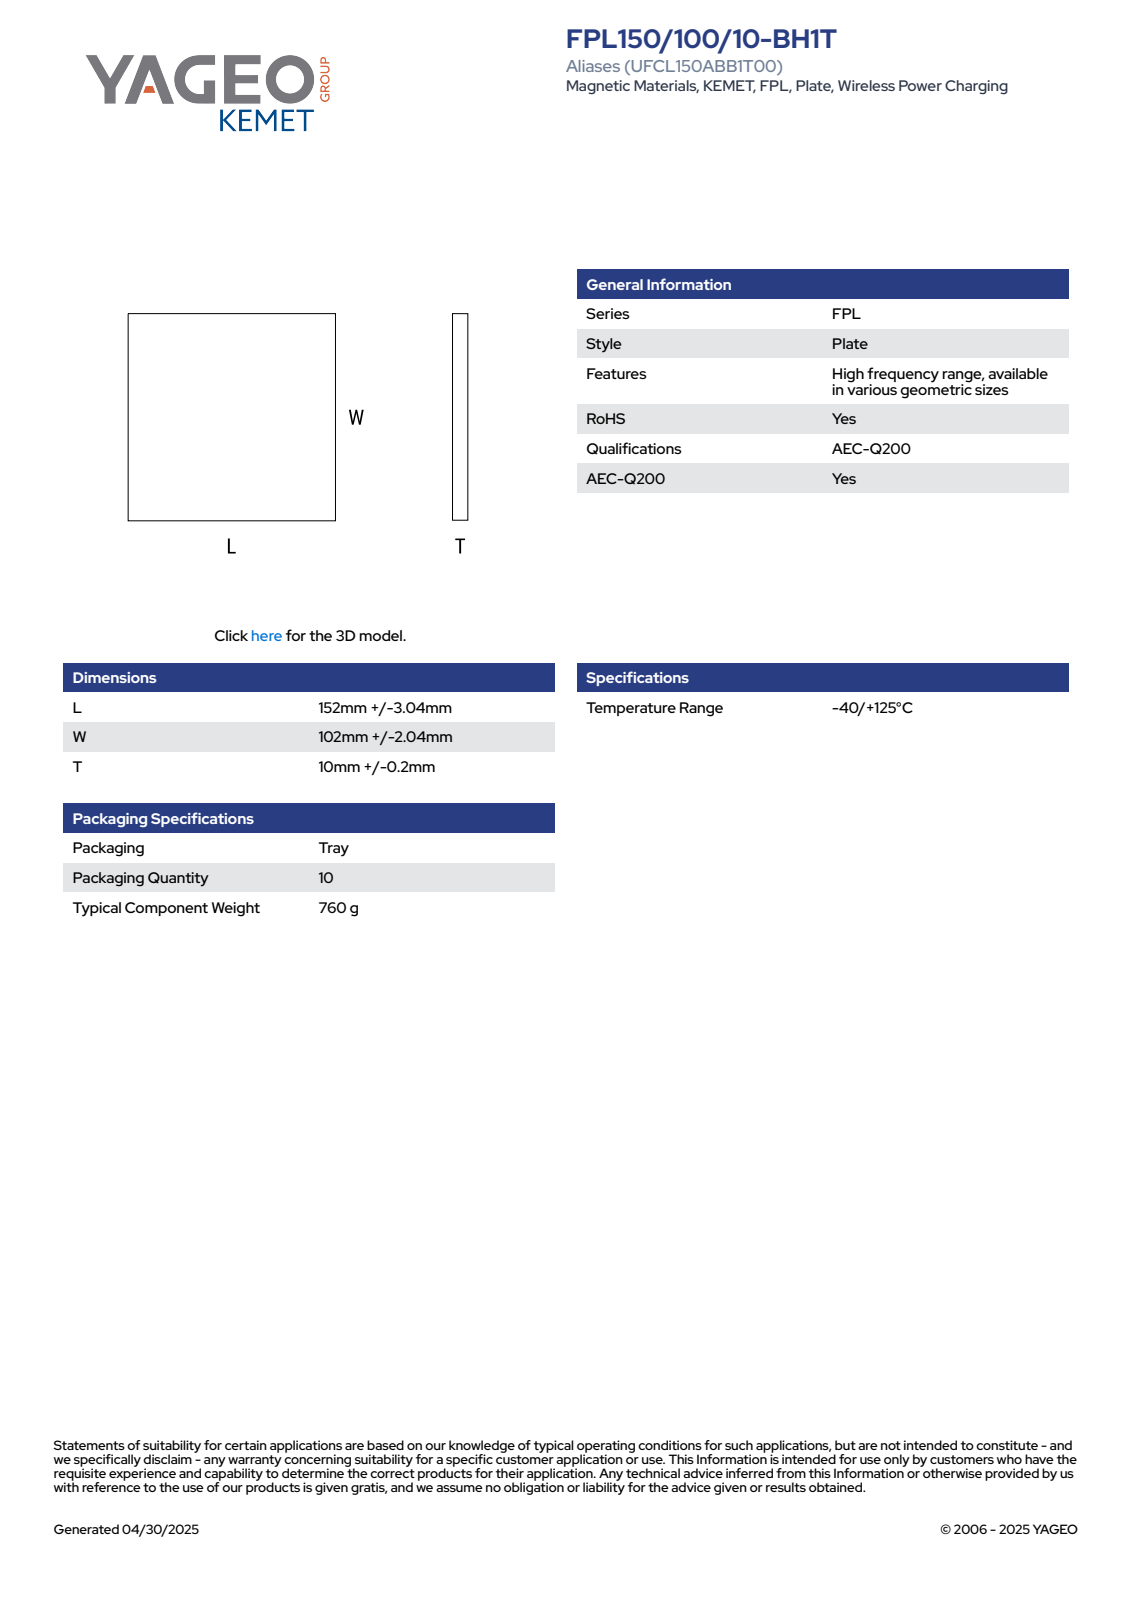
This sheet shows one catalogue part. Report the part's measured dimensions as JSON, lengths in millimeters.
{"part_name": "FM_KP_L155.04W104.04T10.2", "step_written_by": "SolidWorks 2020 (AUTOMOTIVE_DESIGN)", "units": "millimeters", "bodies": {"solids": 4, "faces": 63, "planar": 63, "cylindrical": 0, "other": 0}, "overall_size": [155.04, 104.04, 10.21], "volume_mm3": 164535, "surface_area_mm2": 39555, "face_to_face_distances": [10.2, 104.04, 155.04, 39.88, 64.16, 58.26, 18.38, 45.78, 3.5, 14.88]}
